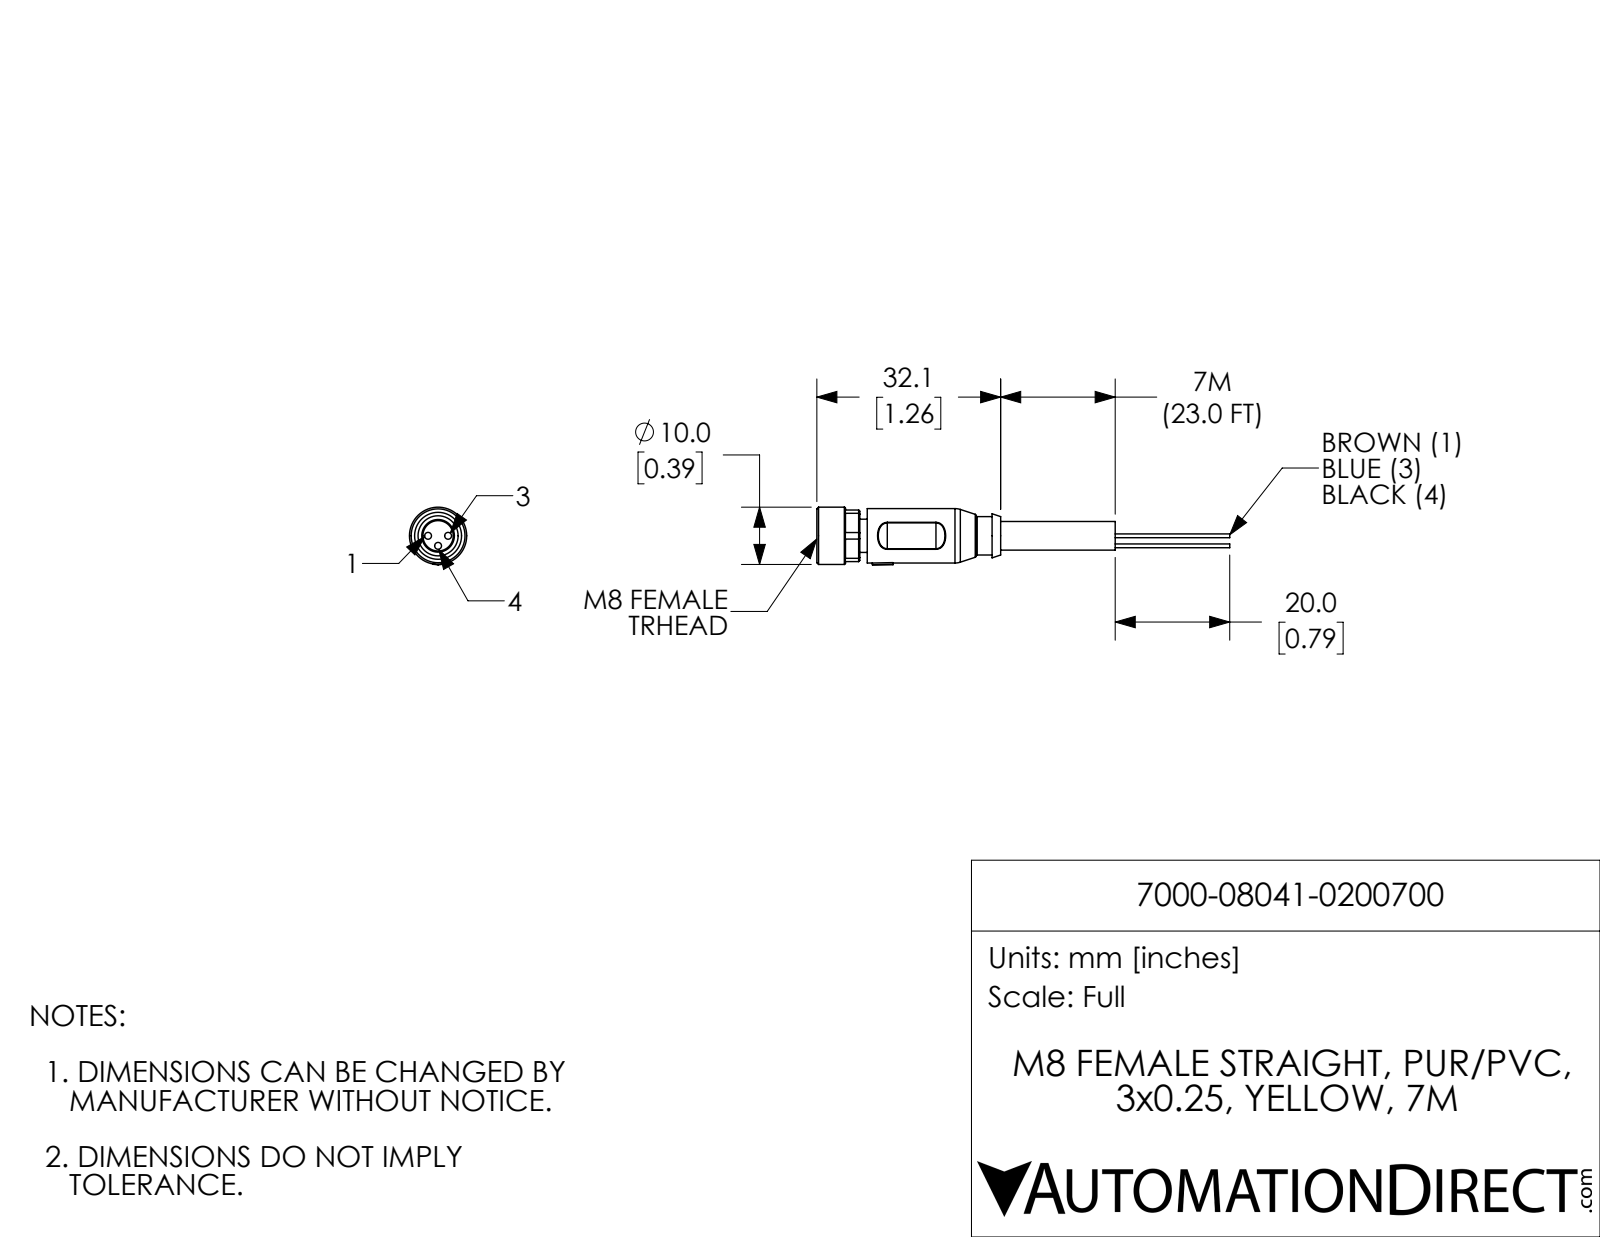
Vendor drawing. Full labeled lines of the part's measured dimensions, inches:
Part name (STEP PRODUCT): 7000-08041-0200700
STEP written by: SolidWorks 2017 (AUTOMOTIVE_DESIGN)
Units: inches
Bodies: 1 solid, 109 faces (36 planar, 42 cylindrical, 31 other)
Overall size (bounding box): 2.839 × 0.396 × 0.394
Volume: 0.141 in³ · Surface area: 2.851 in²
Round holes (diameter × count): ⌀0.047 ×3, ⌀0.276 ×1
Round bosses / shafts (diameter × count): ⌀0.026 ×3, ⌀0.394 ×1, ⌀0.374 ×1, ⌀0.264 ×1, ⌀0.228 ×1, ⌀0.224 ×1, ⌀0.197 ×1
Partial cylindrical surfaces — rounded edges, fillets, slot ends (radius × count): R0.008 ×4, R0.098 ×4, R0.193 ×1, R0.199 ×1
Main face-to-face distances: 0.327, 0.051, 0.969, 0.354, 0.059, 0.028, 0.268, 0.319, 2.024, 1.756
Hole centre spacings: 0.069, 0.097, 0.138
